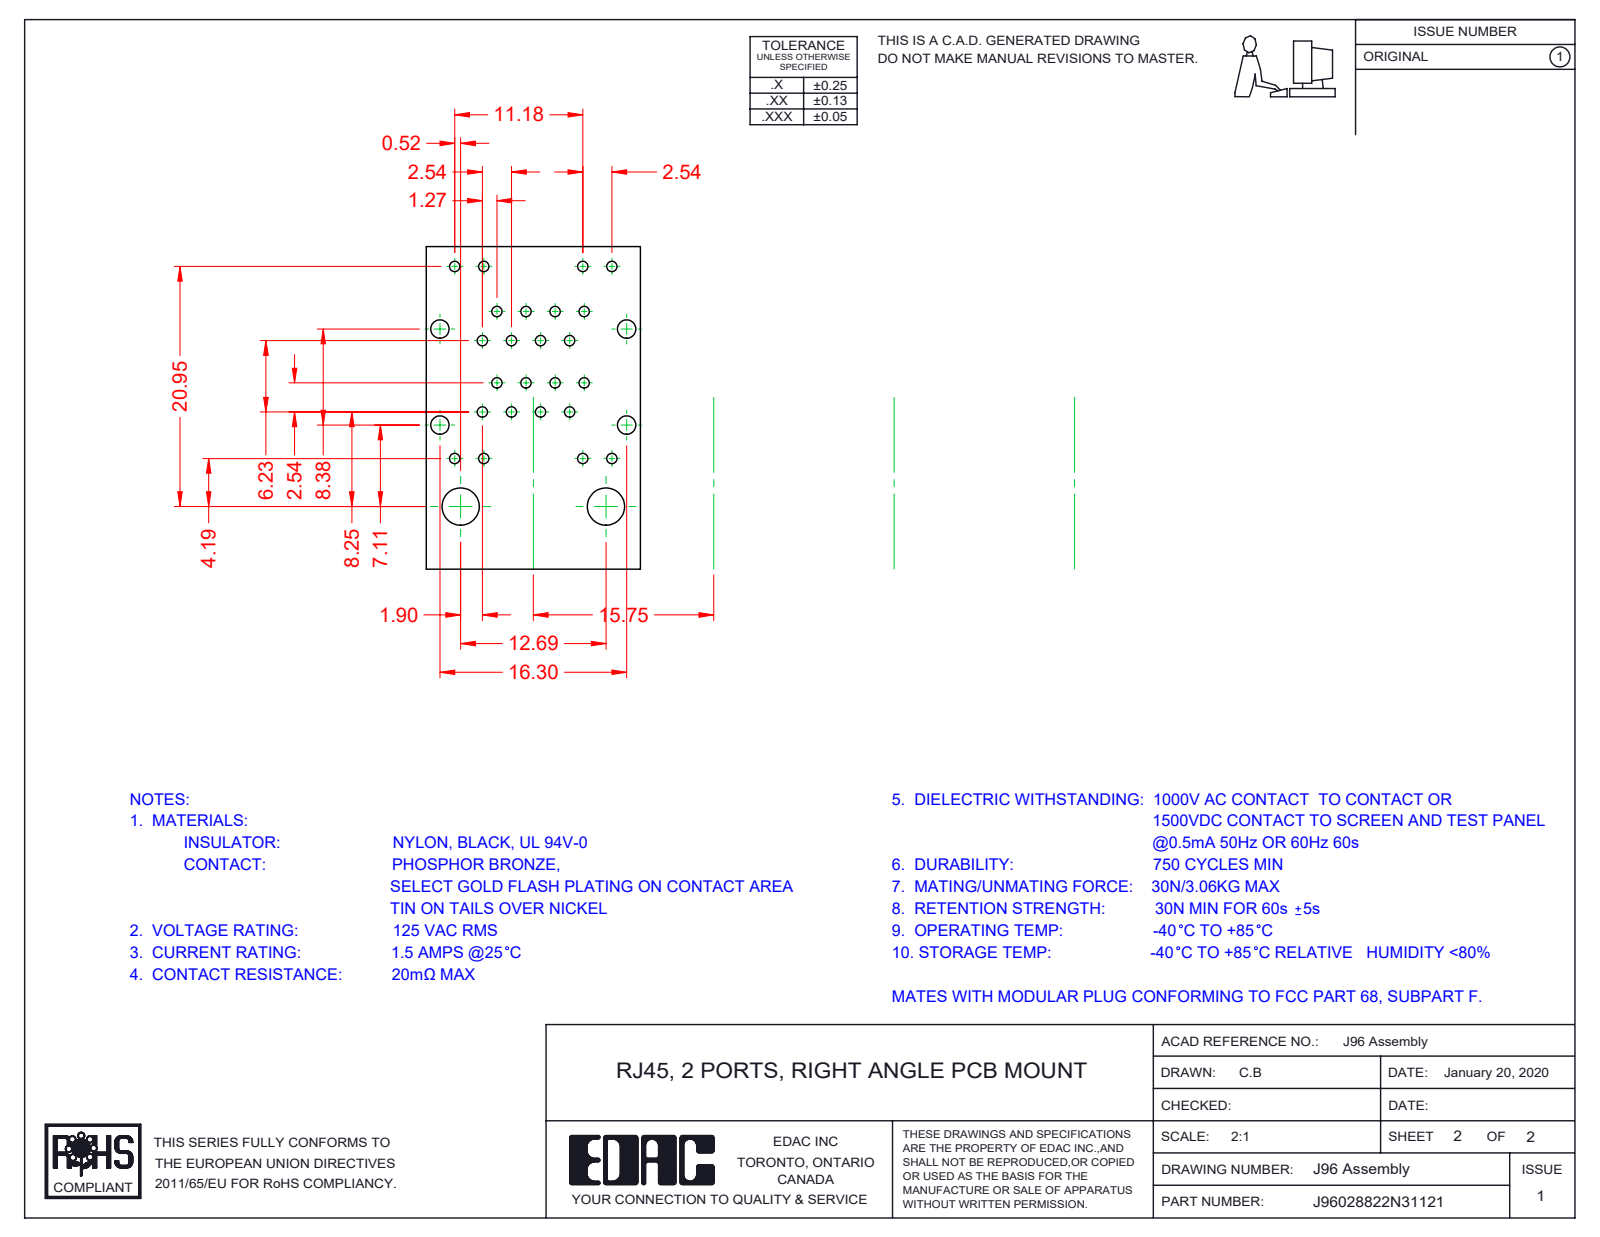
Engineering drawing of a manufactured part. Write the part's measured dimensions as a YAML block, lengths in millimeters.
part_name: "96 Contact Lock Lower; 96 Contacts Lower; 96 Grounding_2 Ports; 96 Shield_2 Ports LED - No EMI (+8 more)"
step_written_by: "SolidWorks 2016 (CONFIG_CONTROL_DESIGN)"
units: millimeters
bodies: {solids: 27, faces: 2382, planar: 1849, cylindrical: 427, other: 106}
overall_size: [29.58, 28.68, 16.8]
volume: 6852
surface_area: 19109
partial_cylinders:
  - {radius: 0.25, count: 48}
  - {radius: 0.15, count: 32}
  - {radius: 0.35, count: 24}
  - {radius: 0.5, count: 16}
  - {radius: 1, count: 16}
  - {radius: 0.2, count: 13}
  - {radius: 0.7, count: 9}
  - {radius: 2, count: 5}
face_to_face_distances: [16.3, 16.1, 1.75, 16.5, 14.75, 1.55, 14.55, 0.53, 1.48, 11.2]
